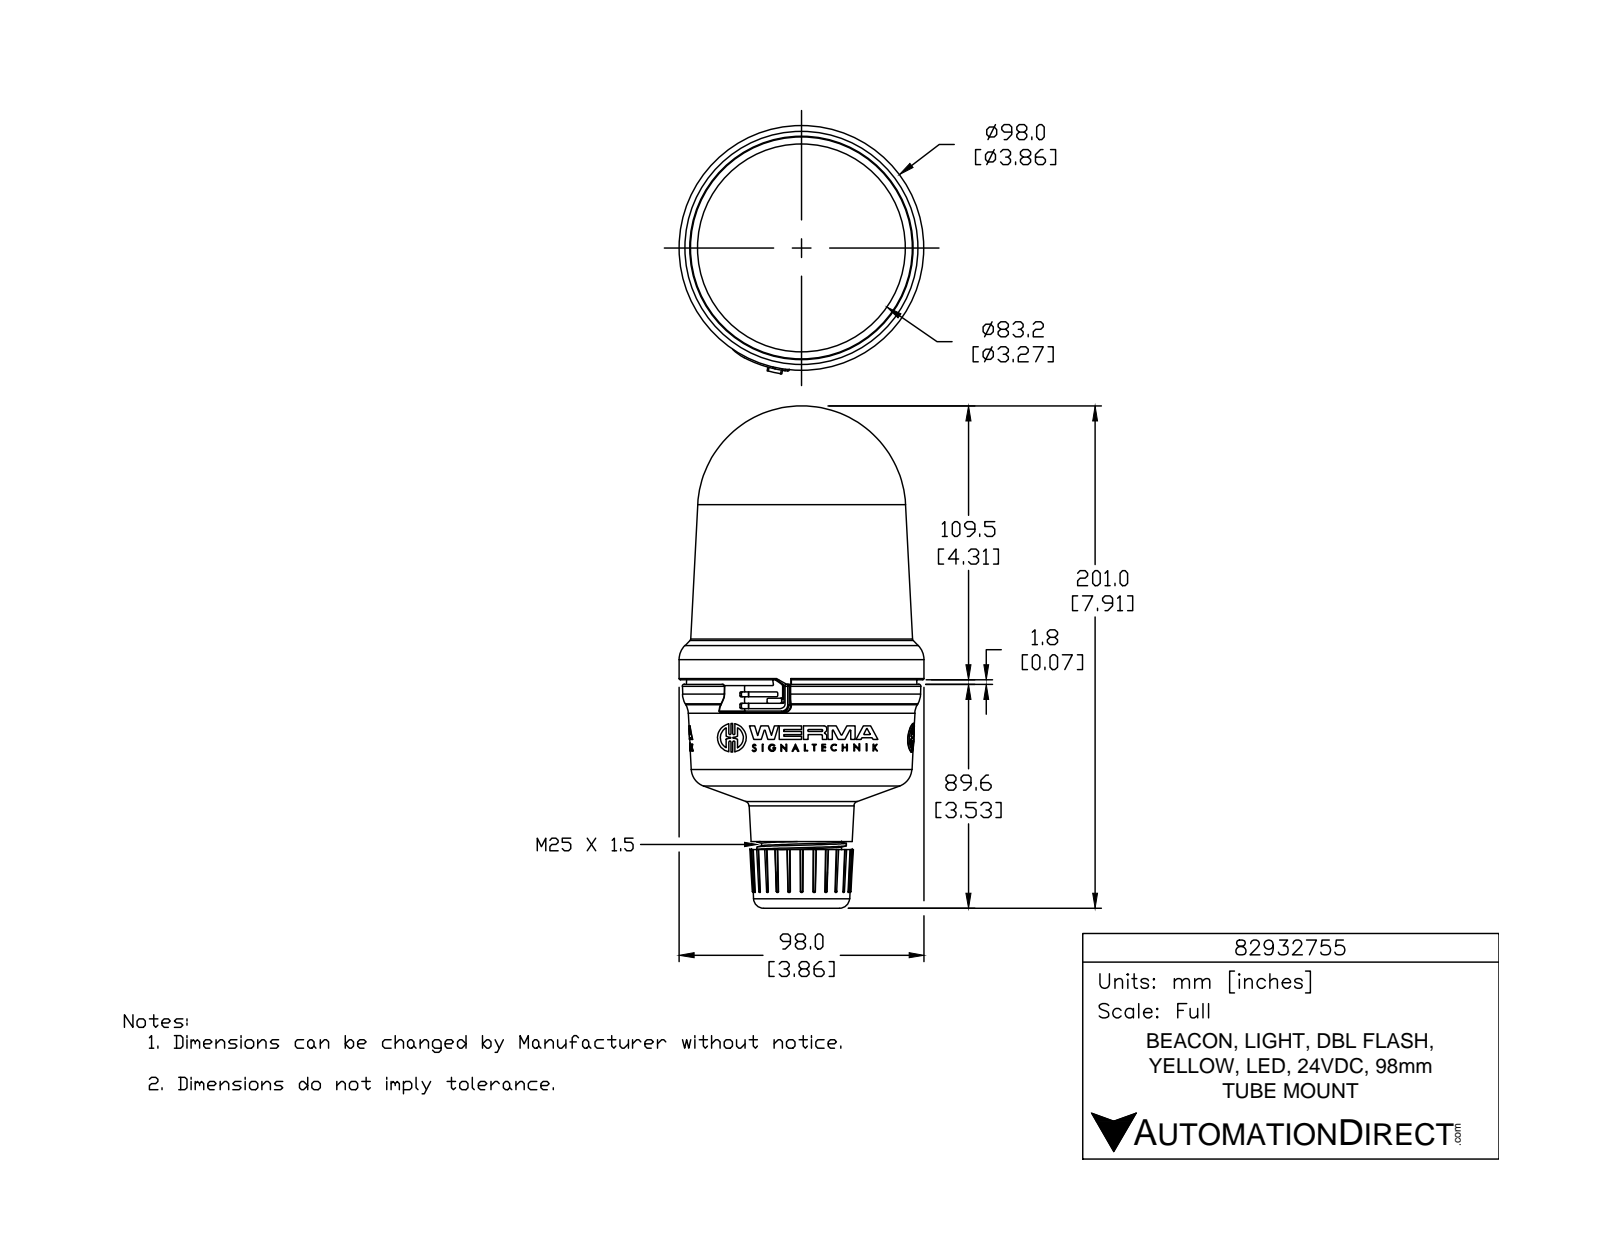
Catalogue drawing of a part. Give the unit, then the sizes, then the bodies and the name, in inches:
Units: inches
Overall size (bounding box): 7.914 × 3.912 × 3.858
Round holes (diameter × count): ⌀0.078 ×3, ⌀1.013 ×1, ⌀1.024 ×1
Round bosses / shafts (diameter × count): ⌀0.452 ×3, ⌀0.113 ×3, ⌀3.858 ×1, ⌀1.409 ×1, ⌀1.261 ×1
Partial cylindrical surfaces — rounded edges, fillets, slot ends (radius × count): R0.02 ×12, R0.007 ×9, R0.007 ×6, R0.016 ×6, R0.016 ×6, R0.016 ×6, R0.262 ×6, R0.006 ×3
Main face-to-face distances: 2.214, 0.462, 2.676, 0.335, 0.127, 2.548, 2.603, 2.476, 2.141, 0.073
Volume: 54.7 in³ · Surface area: 91.39 in²
Bodies: 1 solid, 1006 faces (554 planar, 189 cylindrical, 263 other)
Part name (STEP PRODUCT): 82932755
STEP written by: SolidWorks 2015 (AUTOMOTIVE_DESIGN)
